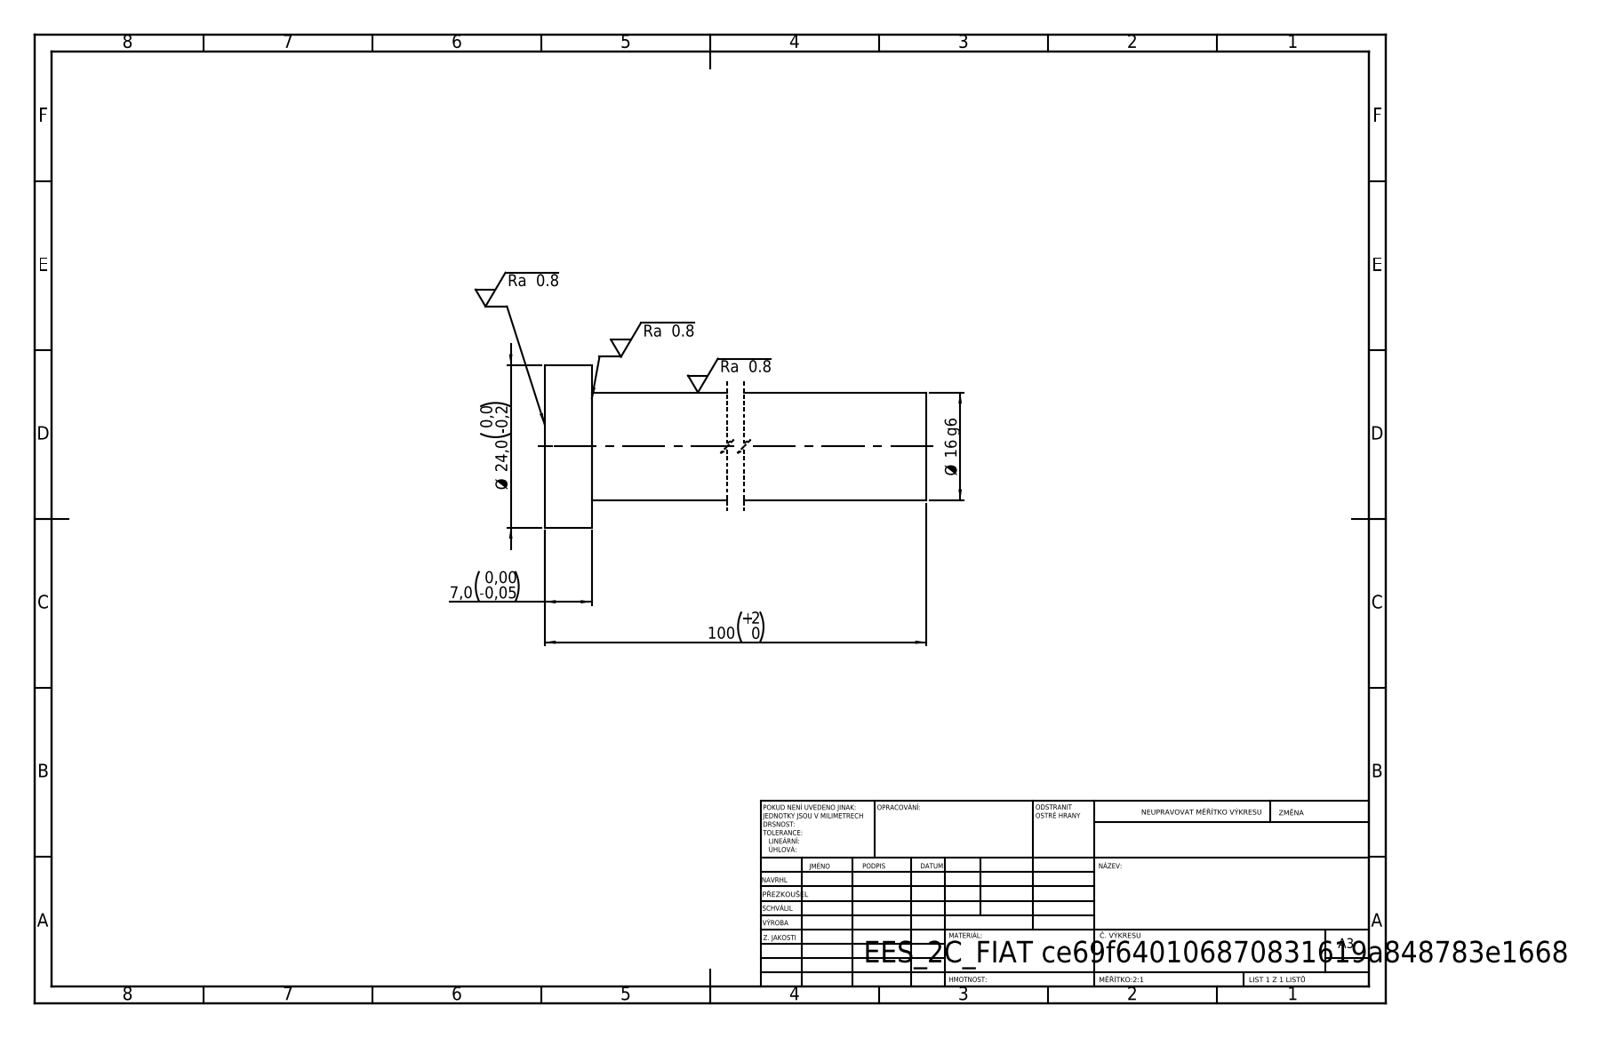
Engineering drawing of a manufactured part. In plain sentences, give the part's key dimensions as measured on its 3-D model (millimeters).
Its 3-D file was written by "SolidWorks 2019 (CONFIG_CONTROL_DESIGN)". It is 1 solid with 7 faces: 3 planar, 4 cylindrical and 0 other. Overall it measures 100 by 24 by 24 millimeters. Its volume is 21 865 cubic millimeters and its surface area 6 107 square millimeters. Round bosses or shafts: 1 of diameter 24, 1 of diameter 16. The main face-to-face distances are 7, 100, 93.
